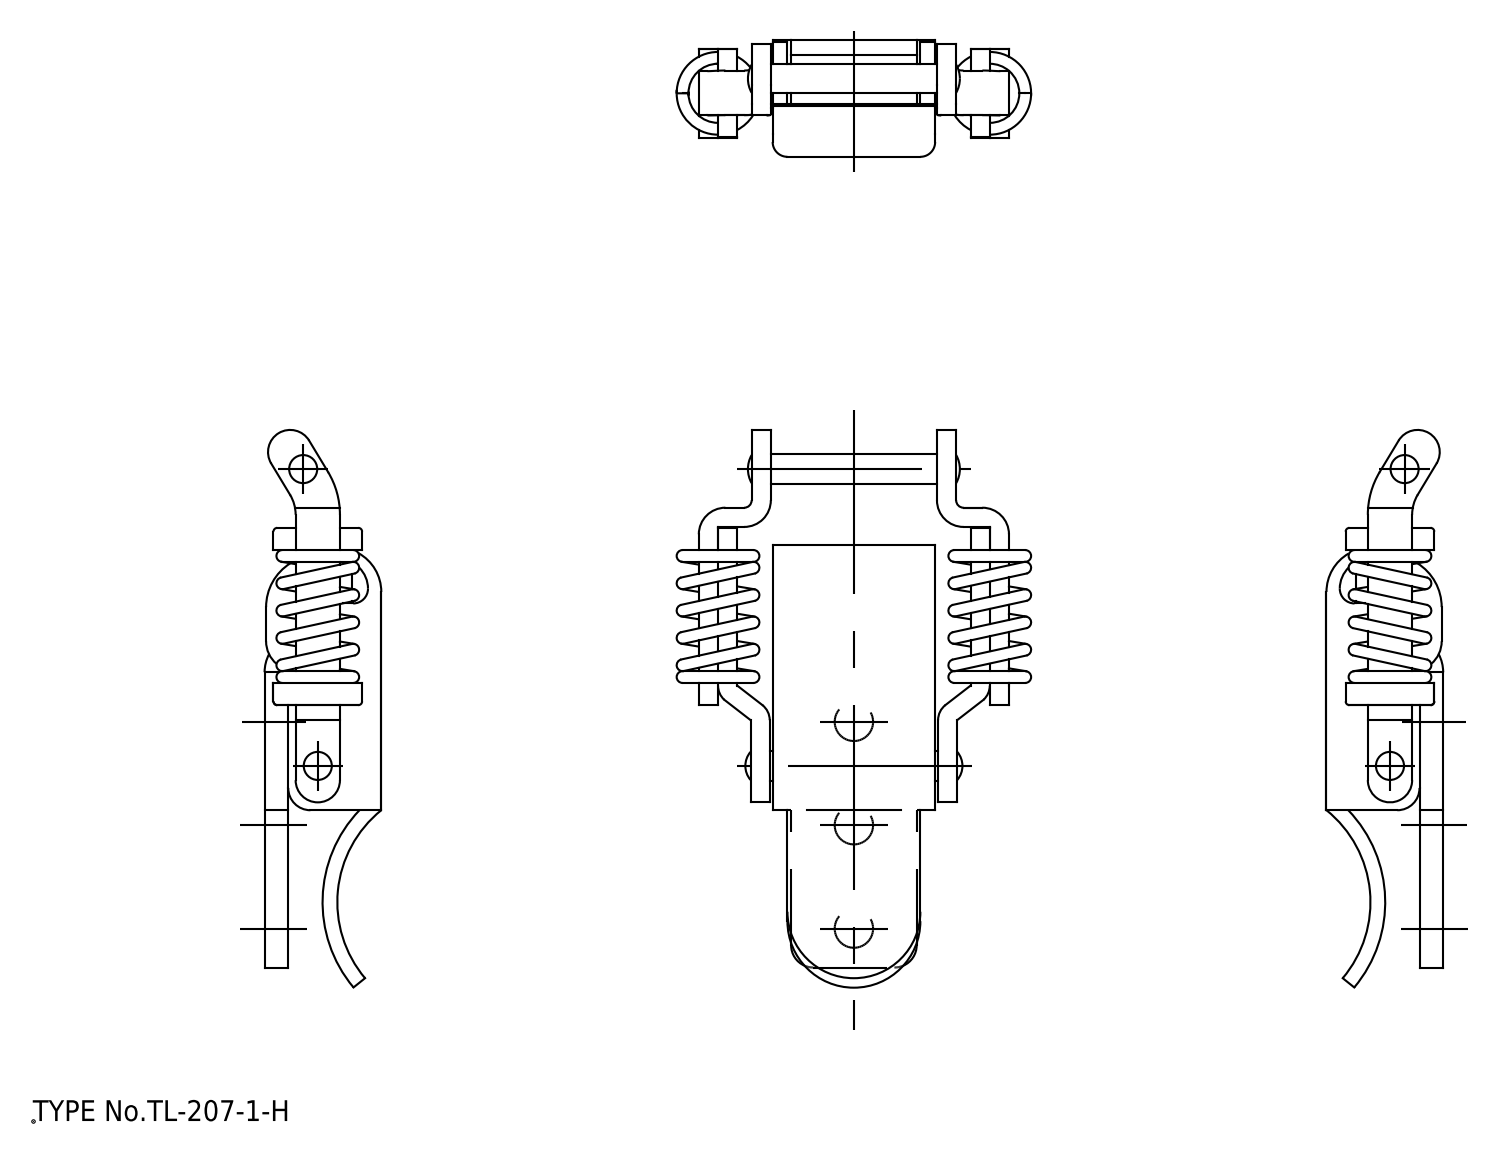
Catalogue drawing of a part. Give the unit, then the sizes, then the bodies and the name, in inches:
Units: inches
Overall size (bounding box): 2.973 × 1.89 × 0.622
Round holes (diameter × count): ⌀0.205 ×3, ⌀0.165 ×1
Round bosses / shafts (diameter × count): ⌀0.157 ×2
Partial cylindrical surfaces — rounded edges, fillets, slot ends (radius × count): R0.079 ×5, R0.118 ×5, R0.02 ×4, R0.102 ×4, R0.142 ×4, R0.039 ×3, R0.157 ×2, R0.205 ×2
Main face-to-face distances: 0.126, 0.102, 0.079, 0.787, 0.291, 0.37, 1.079, 1.157, 1.449, 0.276
Hole centre spacings: 0.551, 1.102
Volume: 0.676 in³ · Surface area: 19.14 in²
Bodies: 8 solids, 212 faces (109 planar, 69 cylindrical, 34 other)
Part name (STEP PRODUCT): ベース; レバー; スプリング; アームA (+1 more)
STEP written by: spGate 19.8.4 (****-****-****-****) (AUTOMOTIVE_DESIGN)
